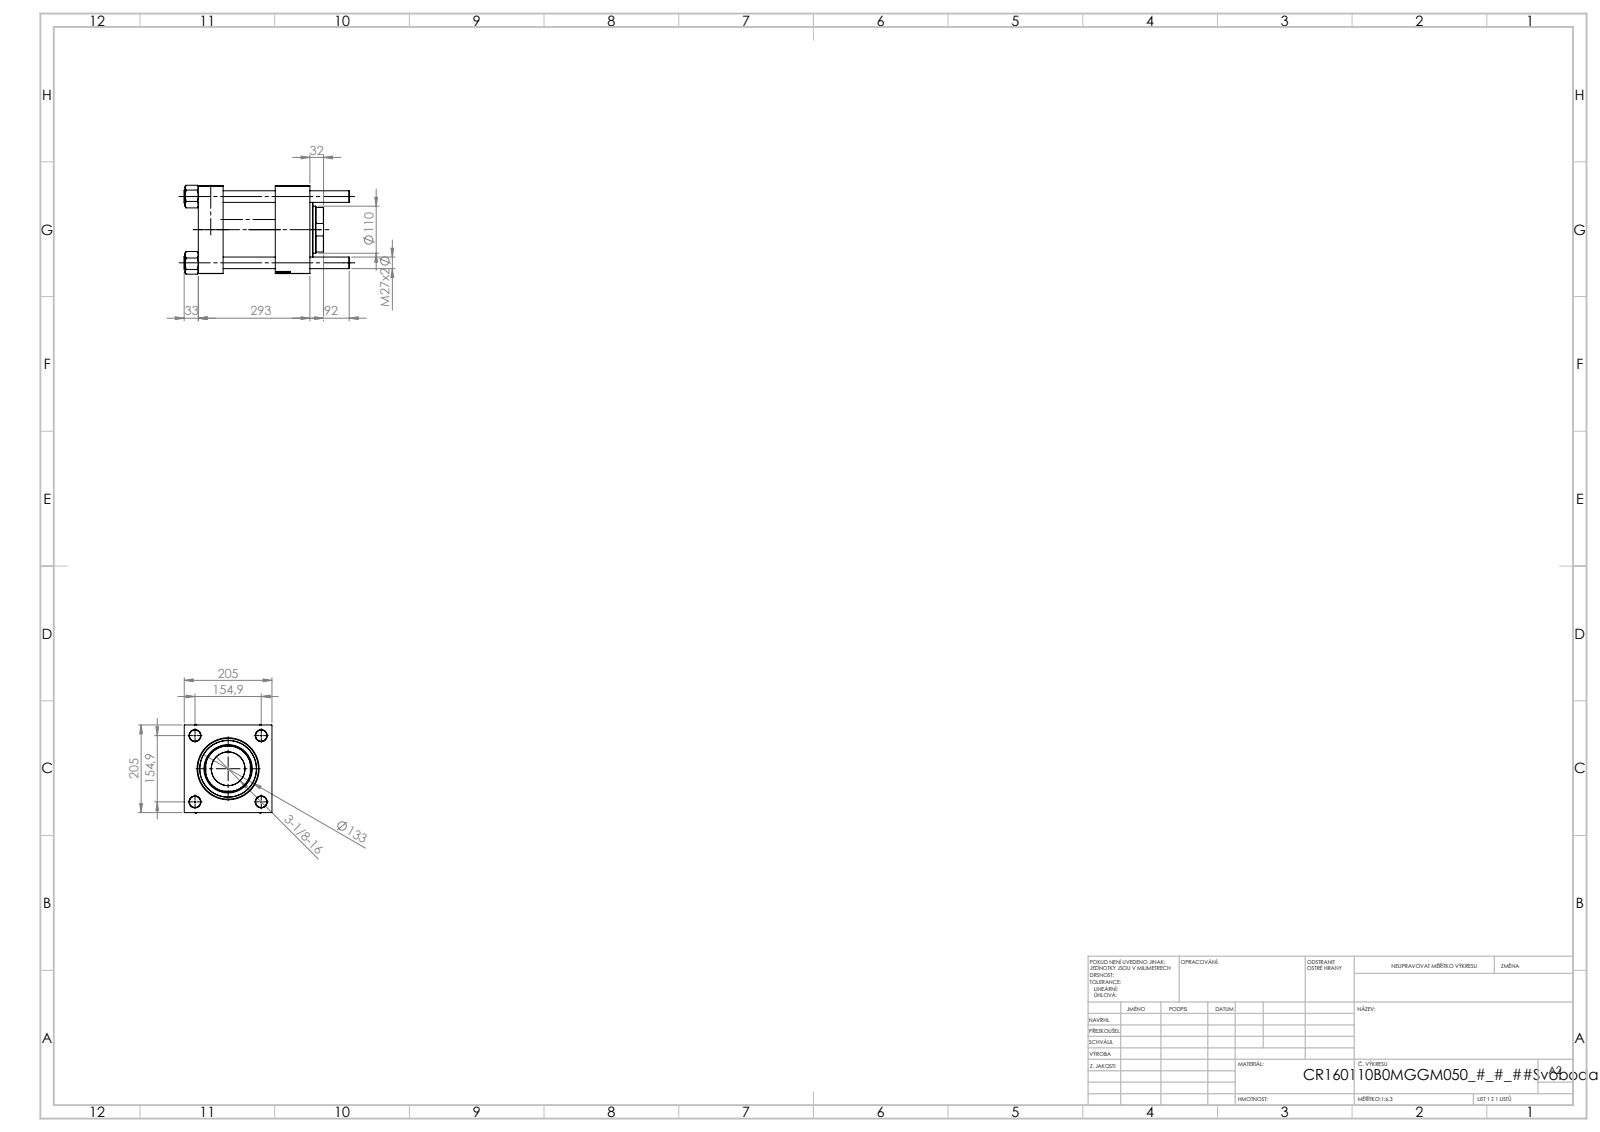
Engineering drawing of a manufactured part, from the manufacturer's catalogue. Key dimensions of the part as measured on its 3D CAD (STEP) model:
Part name (STEP PRODUCT): V215CR_B_TYCINKA; NUT_M5_B; V215CR_VCP_B; V215_VC_A (+1 more)
STEP written by: SolidWorks 2019 (CONFIG_CONTROL_DESIGN)
Units: millimetres
Bodies: 11 solids, 1206 faces (479 planar, 79 cylindrical, 648 other)
Overall size (bounding box): 386 × 207.94 × 205
Volume: 8 352 000 mm³ · Surface area: 833 509 mm²
Round holes (diameter × count): ⌀27 ×5, ⌀7 ×2, ⌀33.24 ×2, ⌀45 ×1, ⌀78.5 ×1, ⌀110 ×1, ⌀113 ×1, ⌀120 ×1, ⌀142 ×1, ⌀160 ×1
Round bosses / shafts (diameter × count): ⌀30 ×4, ⌀166 ×1, ⌀133 ×1
Partial cylindrical surfaces — rounded edges, fillets, slot ends (radius × count): R54 ×1
Main face-to-face distances: 205, 58, 180, 122, 203, 261, 81, 232.3, 174.3, 52.3
Hole centre spacings: 109.53, 154.9, 219.06, 184.24
